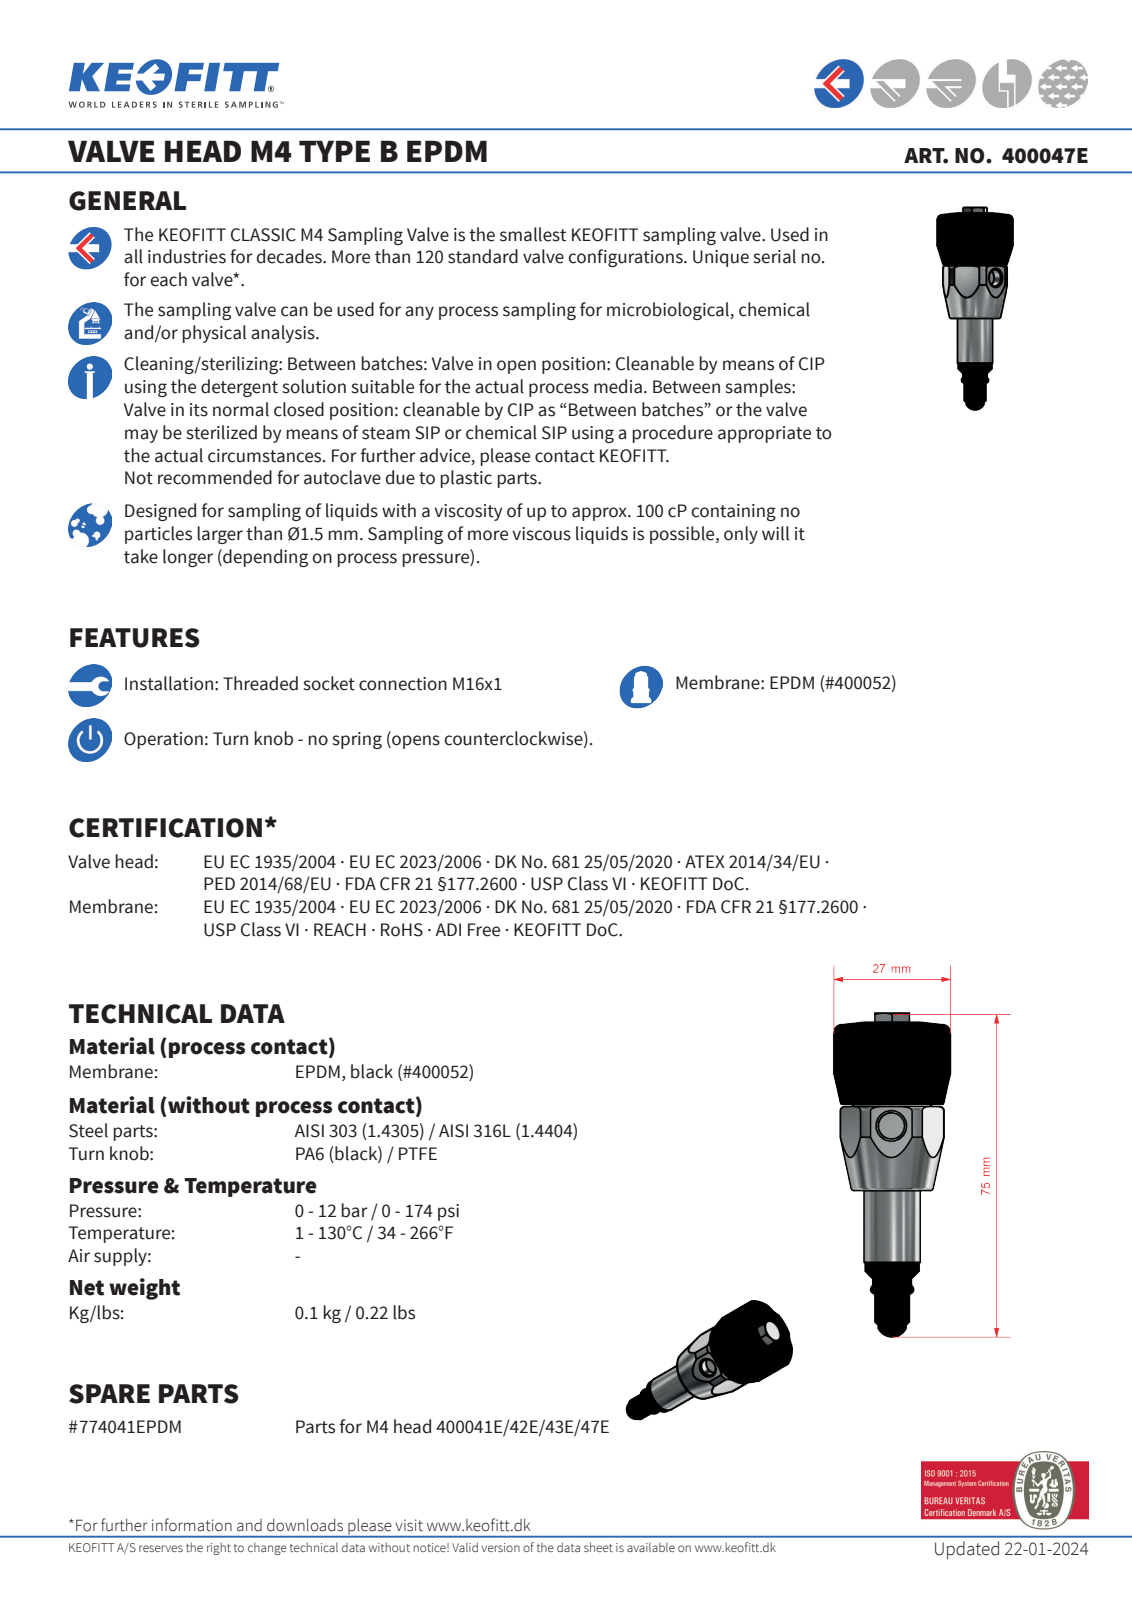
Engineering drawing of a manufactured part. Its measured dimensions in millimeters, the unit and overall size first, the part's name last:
Units: millimetres
Overall size (bounding box): 74.4 × 28 × 26.9
Round holes (diameter × count): ⌀3.05 ×1, ⌀6.1 ×1, ⌀11.55 ×1, ⌀12.5 ×1, ⌀15 ×1
Round bosses / shafts (diameter × count): ⌀17 ×1, ⌀13 ×1, ⌀9 ×1, ⌀8 ×1, ⌀6.5 ×1, ⌀3 ×1
Partial cylindrical surfaces — rounded edges, fillets, slot ends (radius × count): R6 ×6, R12 ×1, R14 ×1
Main face-to-face distances: 22, 0.5, 17.1, 17.6, 3.5, 20.6, 21.1, 8, 19.61, 16.11
Hole centre spacings: 1
Volume: 20 327 mm³ · Surface area: 5 712 mm²
Bodies: 1 solid, 91 faces (20 planar, 30 cylindrical, 41 other)
STEP written by: Autodesk Inventor 2008 (AUTOMOTIVE_DESIGN)
